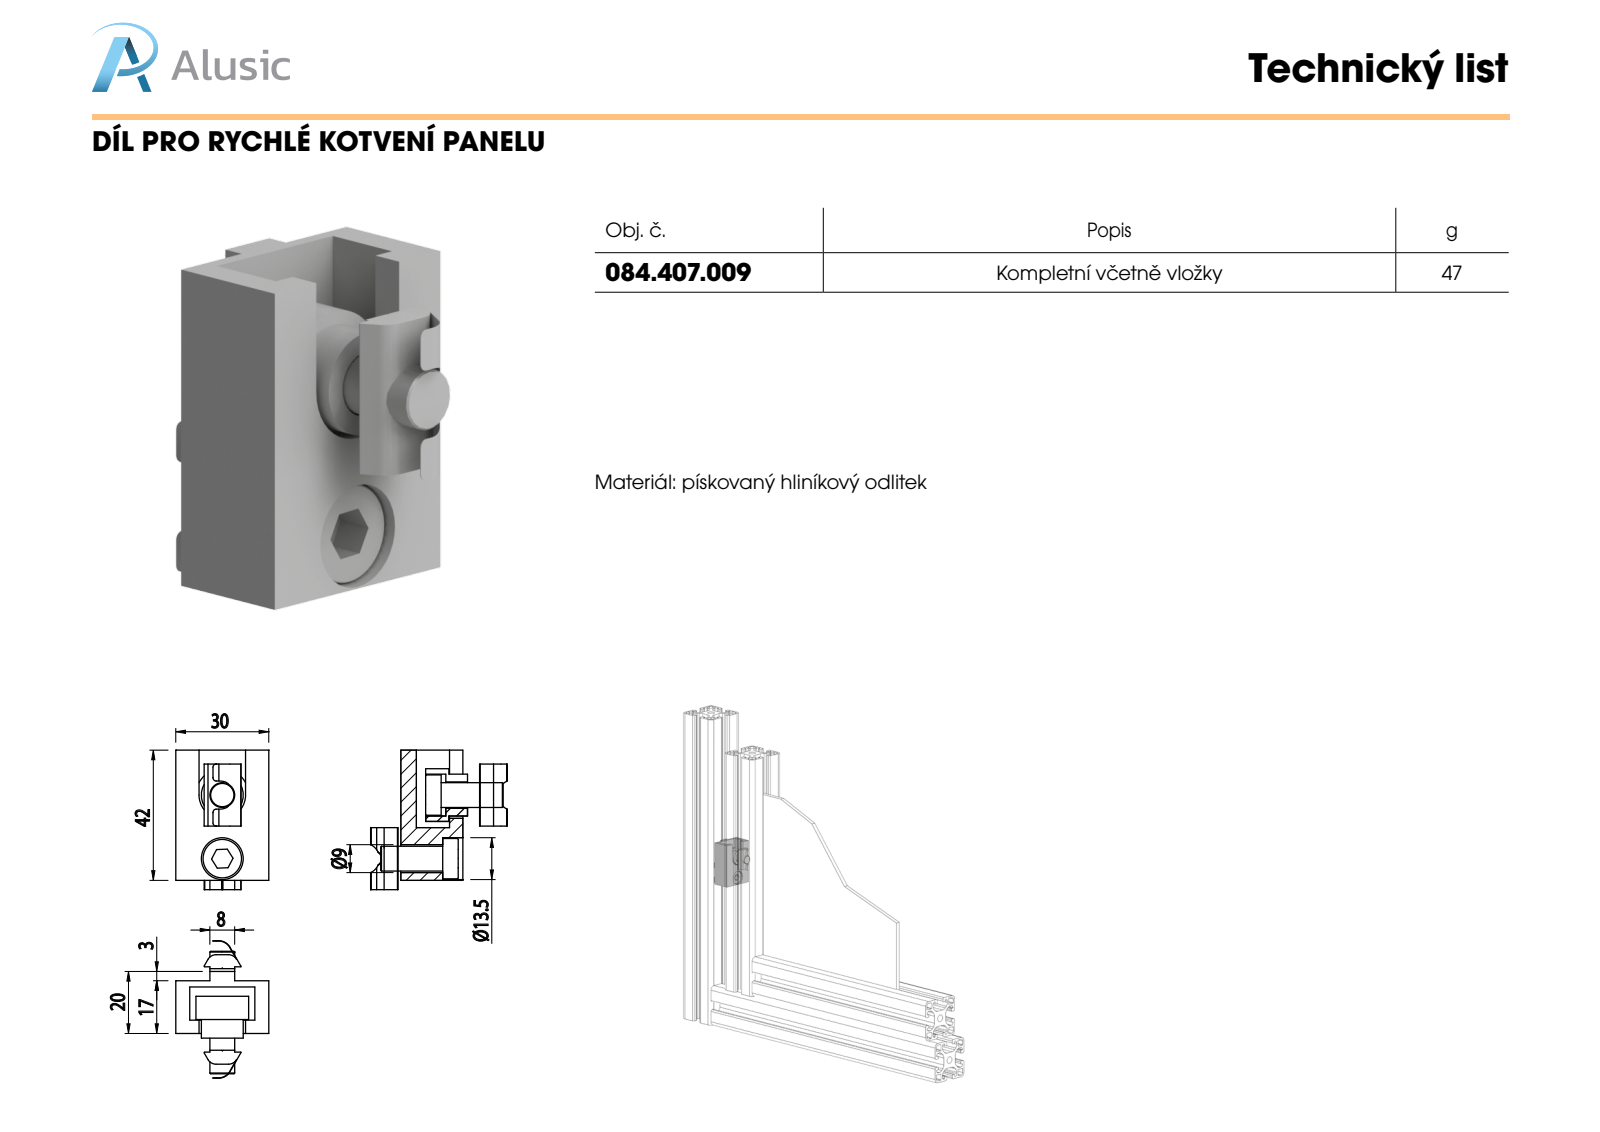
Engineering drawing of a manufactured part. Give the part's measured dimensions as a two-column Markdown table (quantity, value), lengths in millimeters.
| quantity | value |
| --- | --- |
| part name | 084.301.000 VITI ALUSIC_084.301.003; 084.407.009; 084.302.118; 084.407.001a (+1 more) |
| STEP written by | SolidWorks 2016 (CONFIG_CONTROL_DESIGN) |
| units | millimeters |
| bodies | 6 solids, 160 faces (90 planar, 58 cylindrical, 12 other) |
| overall size | 45 × 44.3 × 30 |
| volume | 19 866 mm³ |
| surface area | 12 274 mm² |
| round holes (diameter × count) | 6.8 × 2, 13.5 × 2, 8.5 × 1, 9 × 1 |
| round bosses / shafts (diameter × count) | 13 × 2, 8 × 2, 17 × 1 |
| partial cylindrical surfaces (radius × count) | 0.2 × 4, 1 × 4, 3 × 4, 4 × 2, 4.1 × 2, 5 × 2, 7.5 × 1, 10.5 × 1 |
| main face-to-face distances | 17, 3, 30, 5, 4.5, 6.5, 15, 2, 14.5, 20 |
| hole center spacings | 20.5 |
